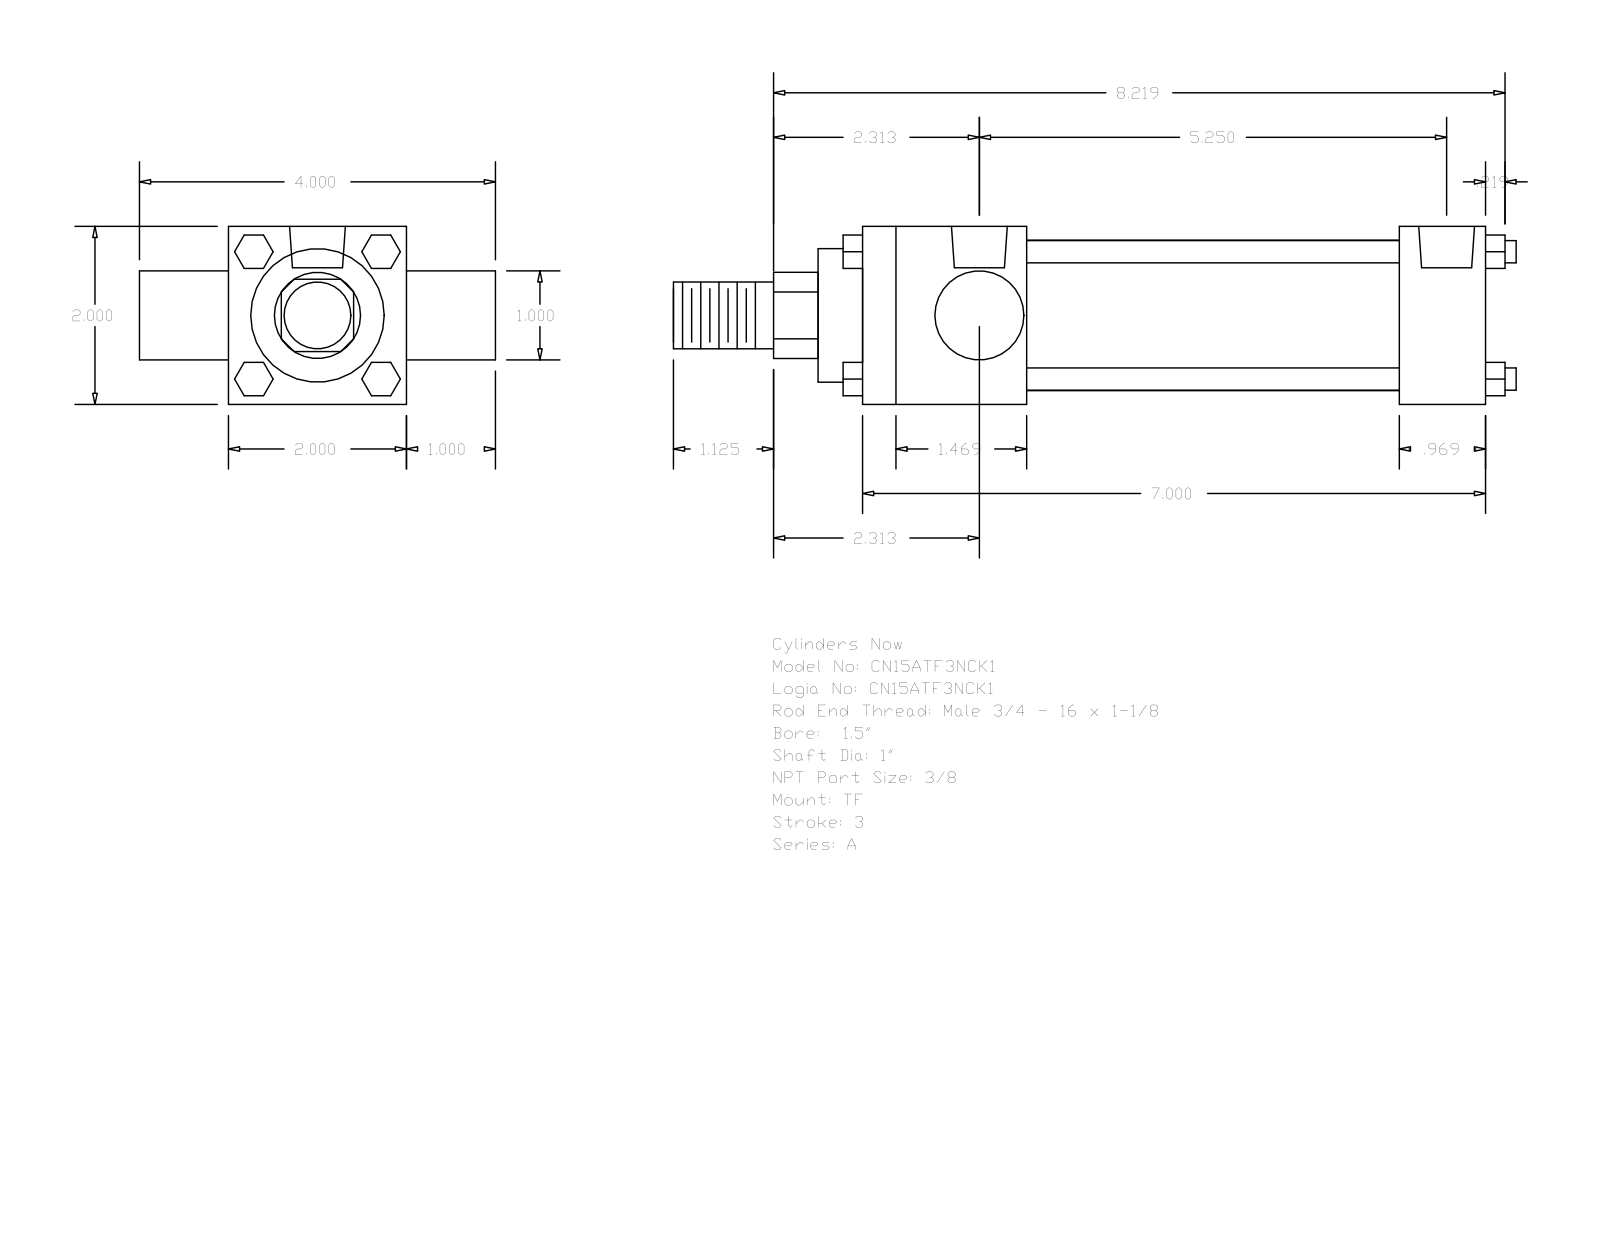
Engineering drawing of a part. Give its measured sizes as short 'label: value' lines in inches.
name: A_TF__0150_1
written by: GSSL Pune (CONFIG_CONTROL_DESIGN)
unit: in
bodies: 0 solids, 120 faces (92 planar, 28 cylindrical, 0 other)
size: 9.469 × 4 × 2
holes: 3× ⌀0.219, 2× ⌀0.627
bosses: 4× ⌀0.25, 2× ⌀1, 1× ⌀1.69, 1× ⌀1.5, 1× ⌀0.75
rounds: 1× R0.484
face distances: 2, 1, 7, 3, 1.844, 6.031, 4.187, 5.156, 0.969, 0.5
hole spacings: 0.156, 5.094, 4.937, 5.25
